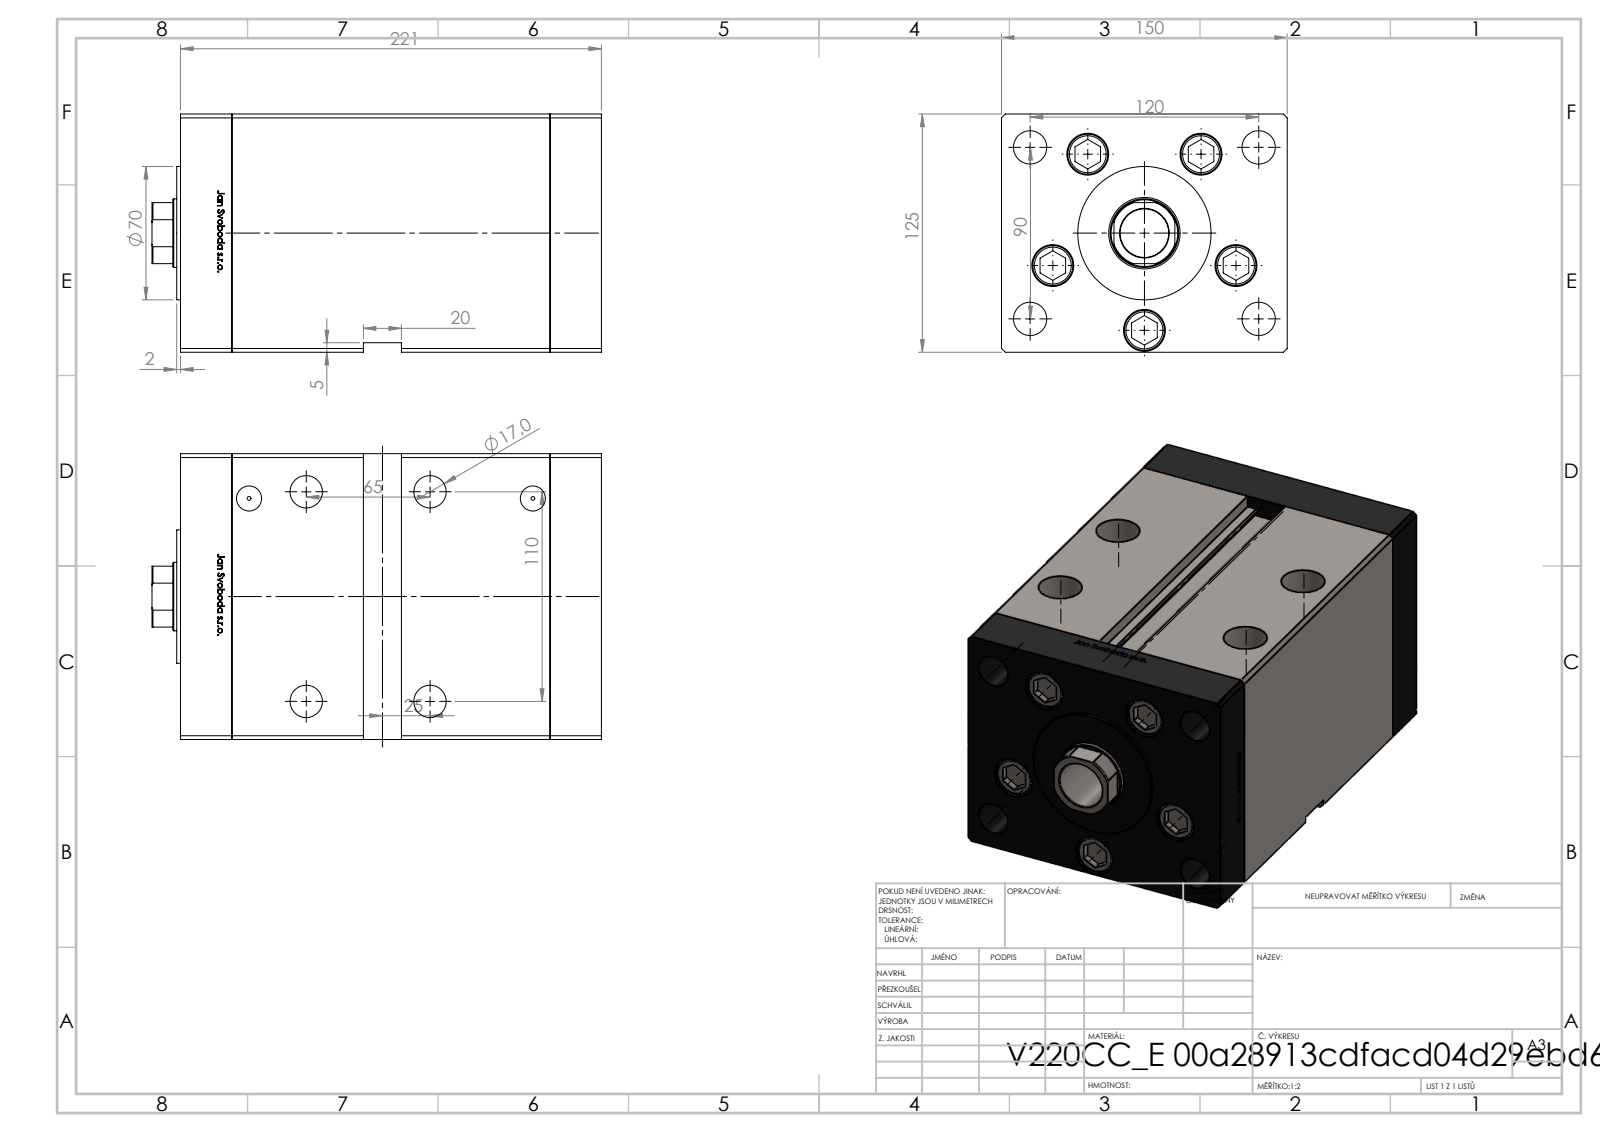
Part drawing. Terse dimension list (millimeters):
name: V220C BACK_E; V220C_FRONT_E; ALLEN BOLT; V220C_VC_E (+1 more)
written by: SolidWorks 2019 (CONFIG_CONTROL_DESIGN)
unit: mm
bodies: 14 solids, 1214 faces (475 planar, 165 cylindrical, 574 other)
size: 236 × 150 × 125
volume: 3 421 000 mm³; area: 396 942 mm²
holes: 9× ⌀17.5, 5× ⌀22, 4× ⌀17, 4× ⌀23, 2× ⌀2, 2× ⌀13.16, 1× ⌀25.5, 1× ⌀36, 1× ⌀37.5
bosses: 5× ⌀21, 5× ⌀8, 1× ⌀80, 1× ⌀70
rounds: 2× R0.93, 1× R17.5
face distances: 27, 194, 167, 125, 150, 33.5, 6.5, 221, 160.5, 187.5
hole spacings: 51, 75, 30.43, 30.48, 58.89, 60.3, 61.25, 63.14
